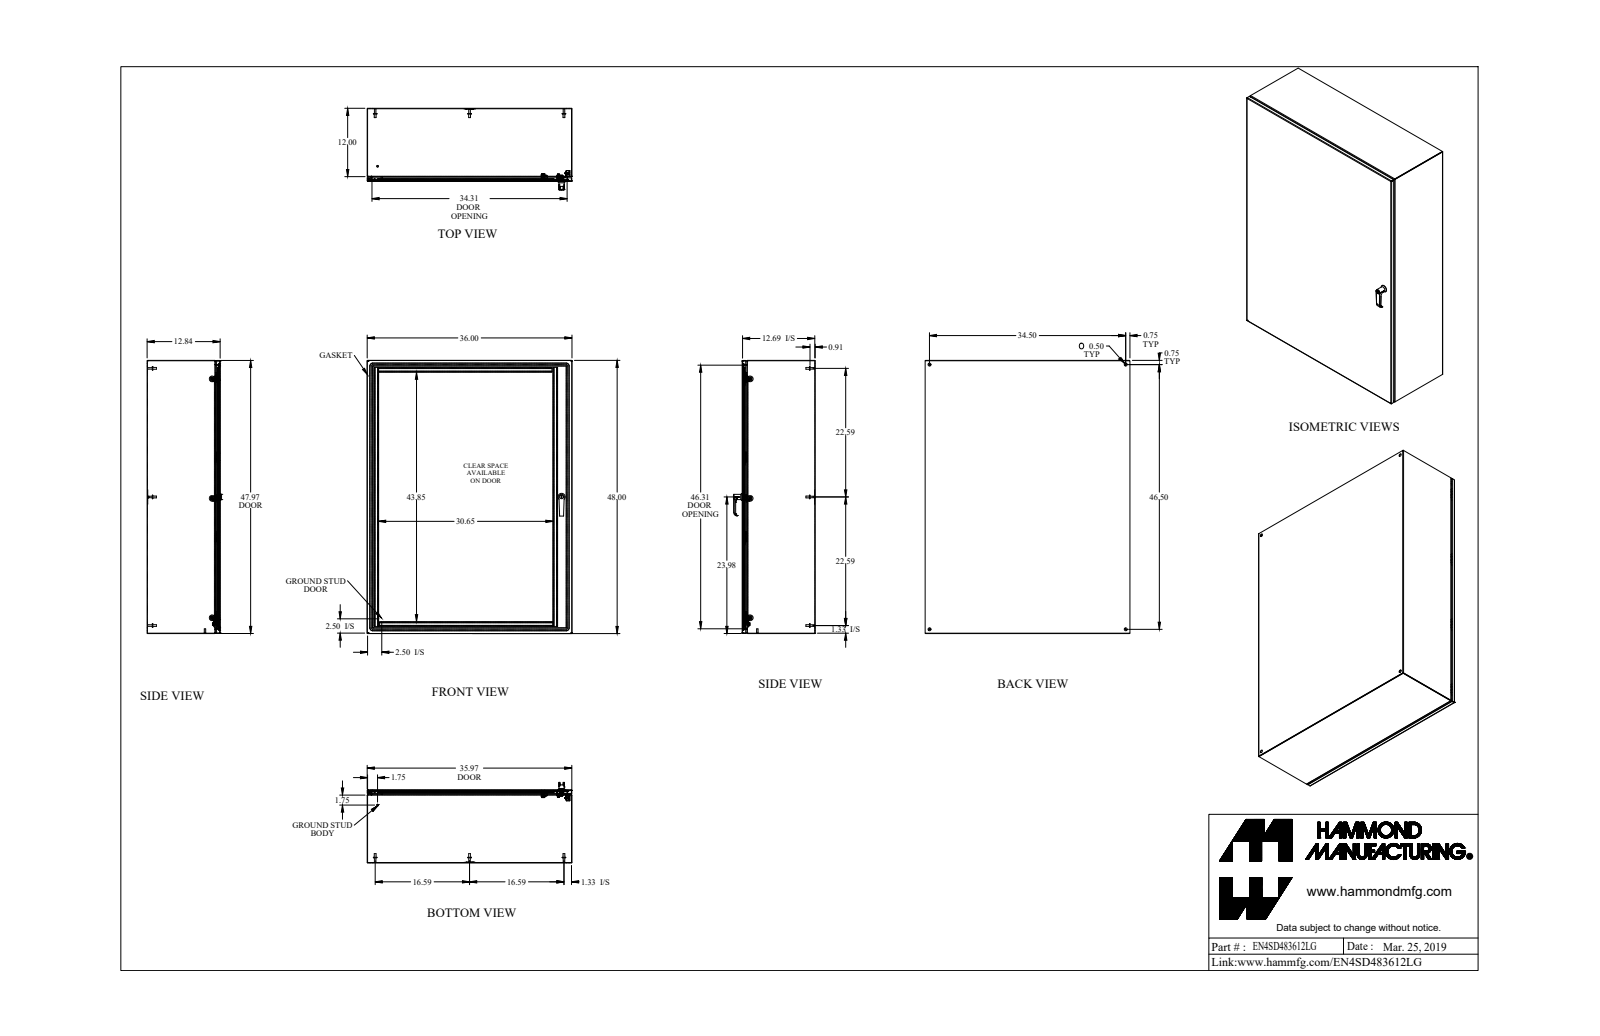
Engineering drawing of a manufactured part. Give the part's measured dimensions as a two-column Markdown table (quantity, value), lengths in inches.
| quantity | value |
| --- | --- |
| part name | EN4SD483612LG |
| STEP written by | SolidWorks 2018 (AUTOMOTIVE_DESIGN) |
| units | inches |
| bodies | 63 solids, 1719 faces (757 planar, 632 cylindrical, 330 other) |
| overall size | 48 × 36 × 14.367 |
| volume | 454.7 in³ |
| surface area | 12 724 in² |
| round holes (diameter × count) | 0.176 × 6, 0.196 × 4, 0.5 × 4, 0.25 × 3, 0.265 × 3, 0.413 × 3, 0.242 × 2, 0.256 × 2, 0.313 × 2, 0.394 × 2, 0.172 × 1, 0.24 × 1 |
| round bosses / shafts (diameter × count) | 0.313 × 8, 0.27 × 8, 0.25 × 8, 0.625 × 6, 0.375 × 6, 0.156 × 6, 1 × 3, 0.625 × 3 |
| partial cylindrical surfaces (radius × count) | 0.043 × 24, 0.081 × 24, 0.036 × 18, 0.108 × 18, 0.062 × 17, 0.03 × 15, 0.094 × 10, 0.016 × 9 |
| main face-to-face distances | 0.072, 12.765, 12.693, 12.837, 35.928, 35.856, 36, 0.072, 47.856, 47.928 |
| hole center spacings | 41.969, 20.981, 20.988, 0.787, 21, 33.504, 34.5, 46.5 |
